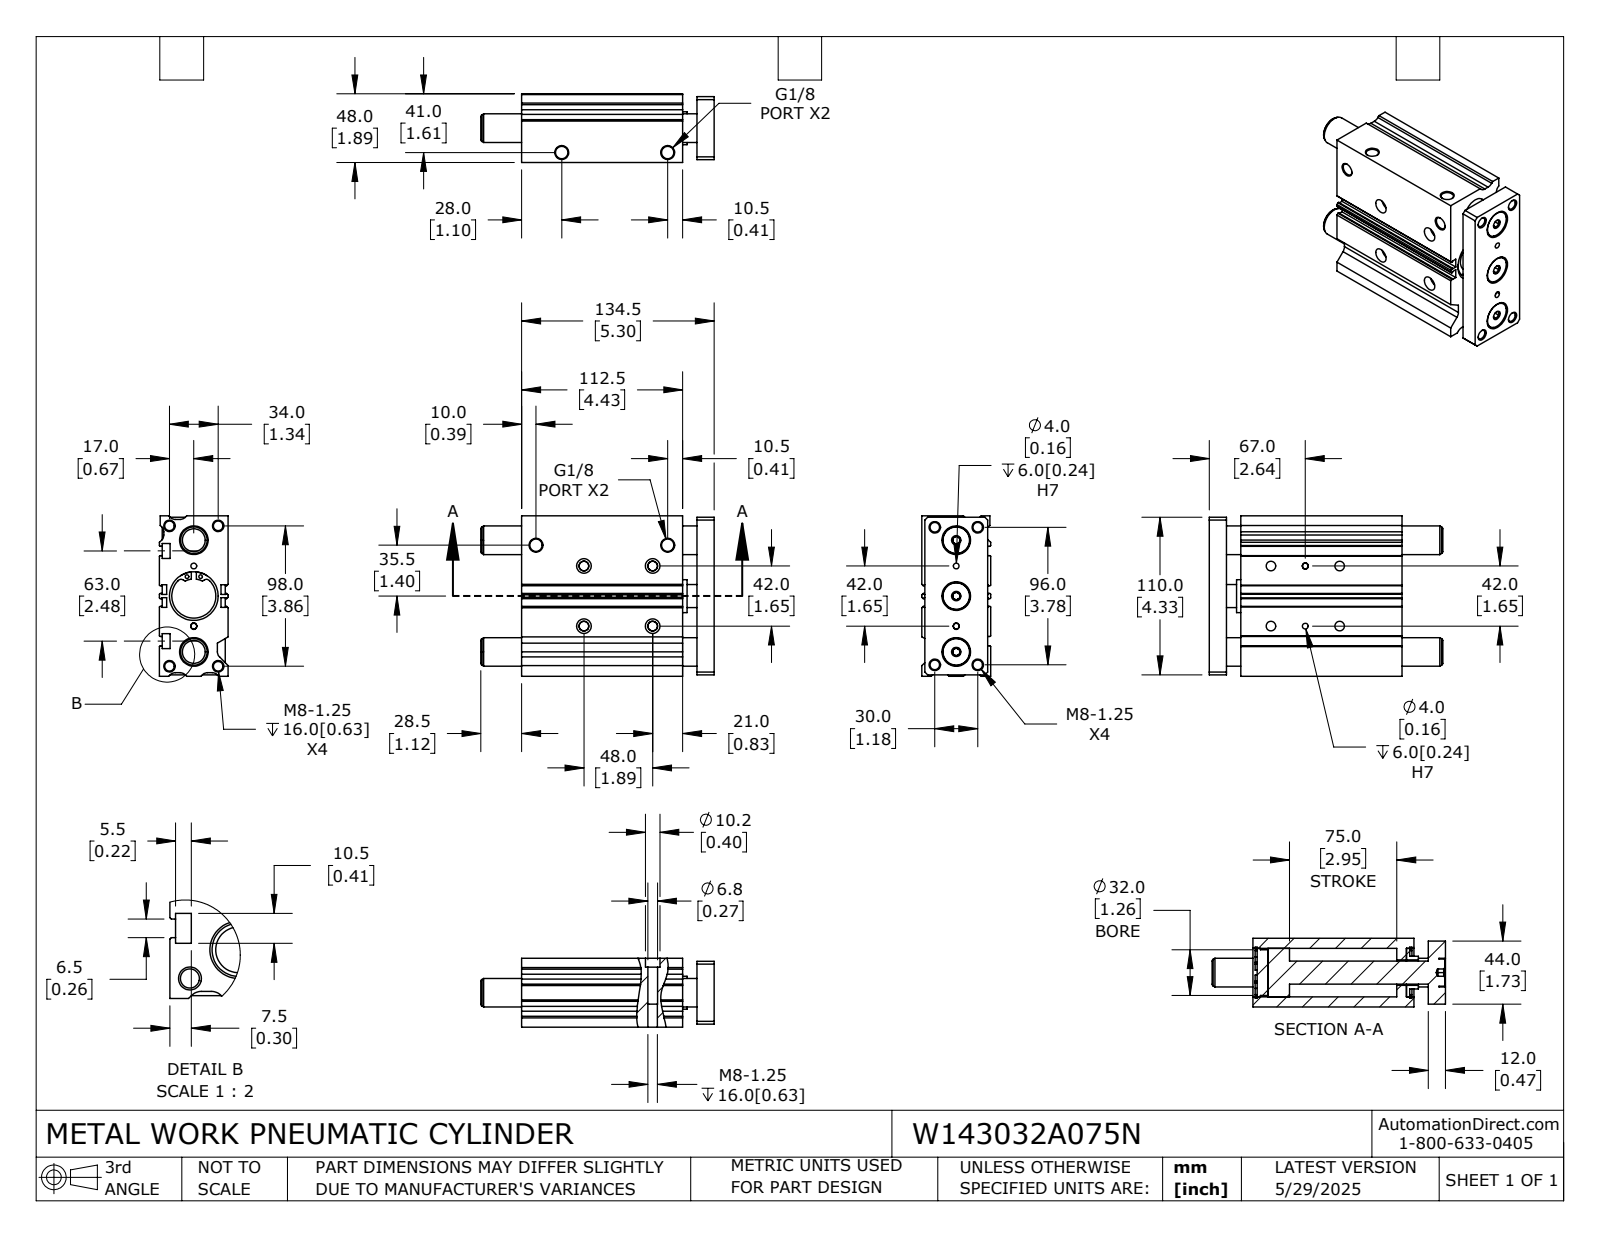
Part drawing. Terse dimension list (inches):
name: W143032A075N_BODY; W143032A075N_ROD; W143032A075N
written by: SolidWorks 2024 (CONFIG_CONTROL_DESIGN)
unit: in
bodies: 6 solids, 394 faces (195 planar, 149 cylindrical, 50 other)
size: 6.417 × 4.409 × 1.89
volume: 34.34 in³; area: 213.6 in²
holes: 12× ⌀0.262, 4× ⌀0.098, 4× ⌀0.157, 4× ⌀0.268, 4× ⌀0.337, 4× ⌀0.402, 3× ⌀0.197, 3× ⌀0.787, 1× ⌀0.697, 1× ⌀1.211
bosses: 3× ⌀0.748, 2× ⌀1.406, 1× ⌀1.339, 1× ⌀1.26, 1× ⌀0.906, 1× ⌀0.63
rounds: 9× R0.197, 4× R0.079, 4× R0.118, 2× R0.507
face distances: 1.89, 0.118, 0.295, 0.472, 4.409, 0.079, 0.866, 0.098, 1.811, 4.311
hole spacings: 0.088, 0.348, 0.566, 0.689, 0.776, 0.945, 1.019, 1.216
